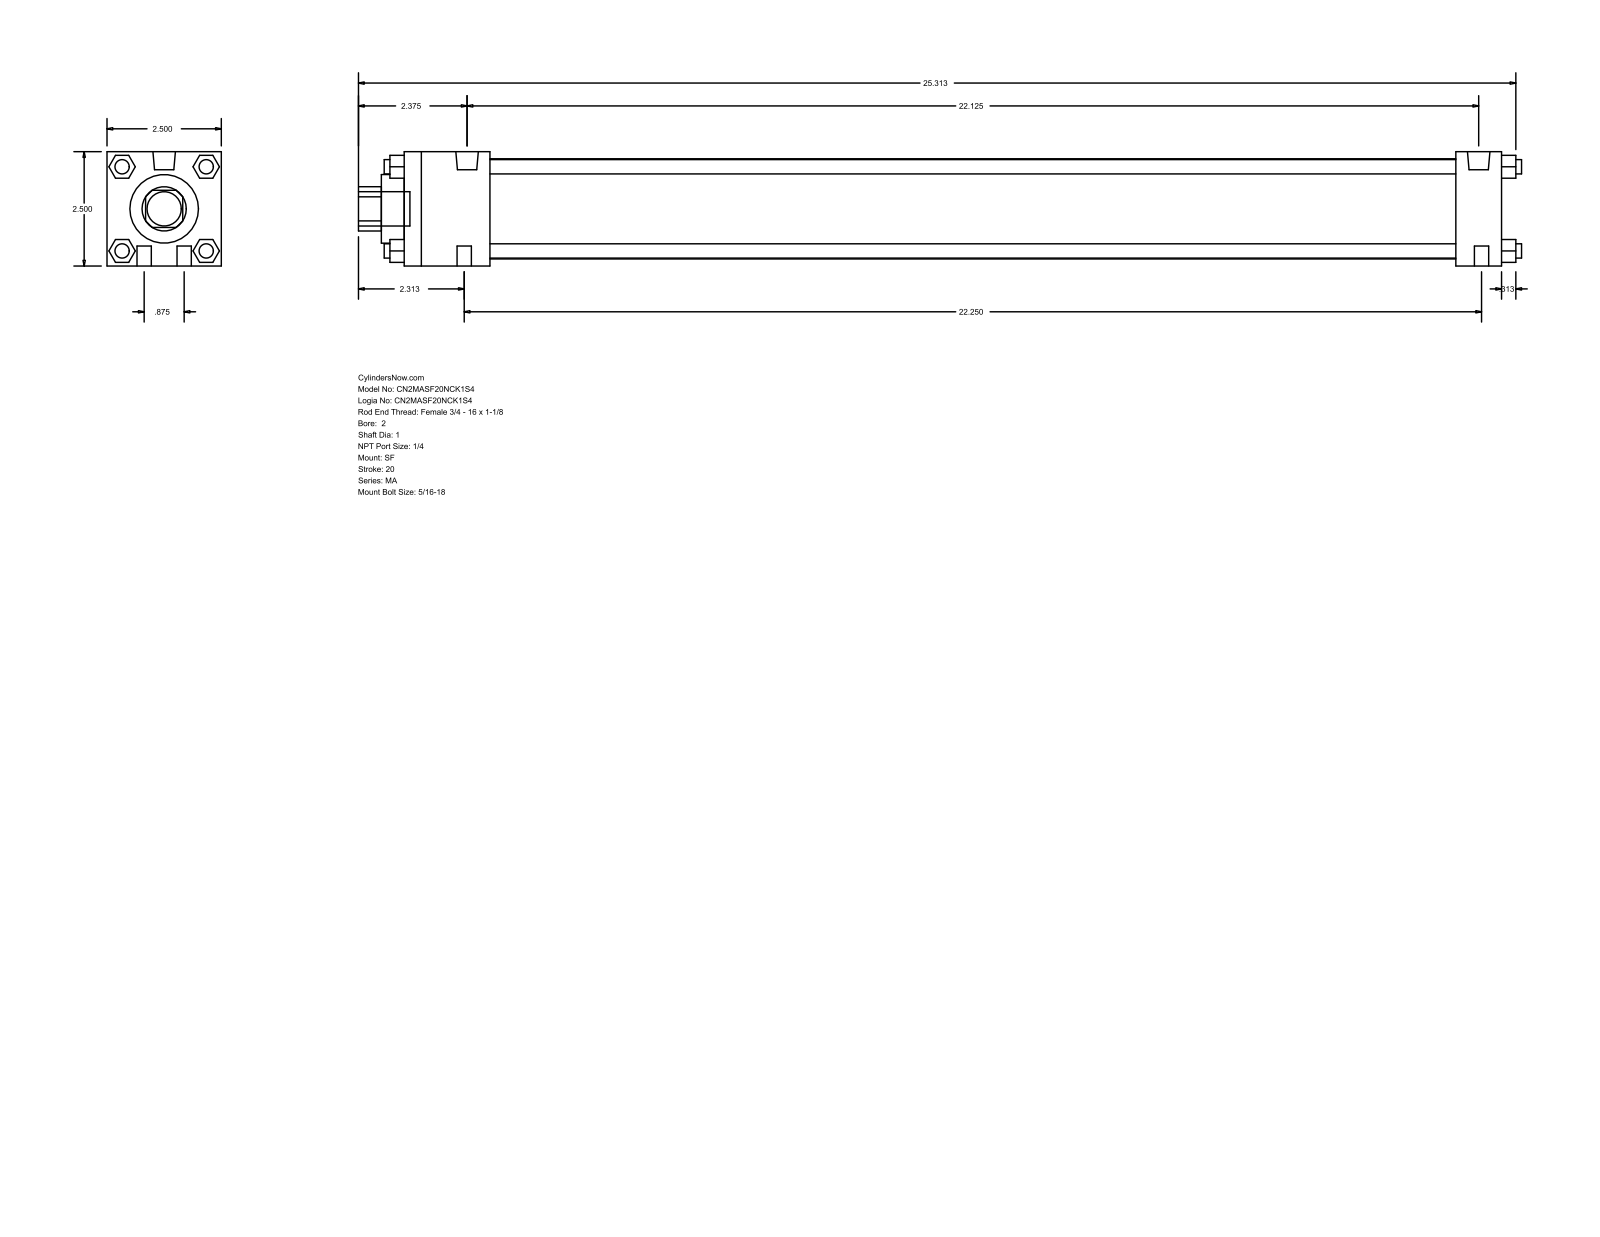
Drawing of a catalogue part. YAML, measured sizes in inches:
part_name: "MA_SF__0200_1"
step_written_by: "GSSL Pune (CONFIG_CONTROL_DESIGN)"
units: inches
bodies: {solids: 0, faces: 124, planar: 94, cylindrical: 30, other: 0}
overall_size: [25.437, 2.5, 2.5]
round_holes:
  - {diameter: 1, count: 1}
  - {diameter: 1.5, count: 1}
  - {diameter: 2.19, count: 1}
round_bosses_or_shafts:
  - {diameter: 0.313, count: 10}
  - {diameter: 0.492, count: 2}
  - {diameter: 0.75, count: 1}
partial_cylinders:
  - {radius: 0.484, count: 1}
face_to_face_distances: [2.5, 24, 0.5, 1, 23, 1.875, 21.125, 22.125, 0.92, 1.593]
